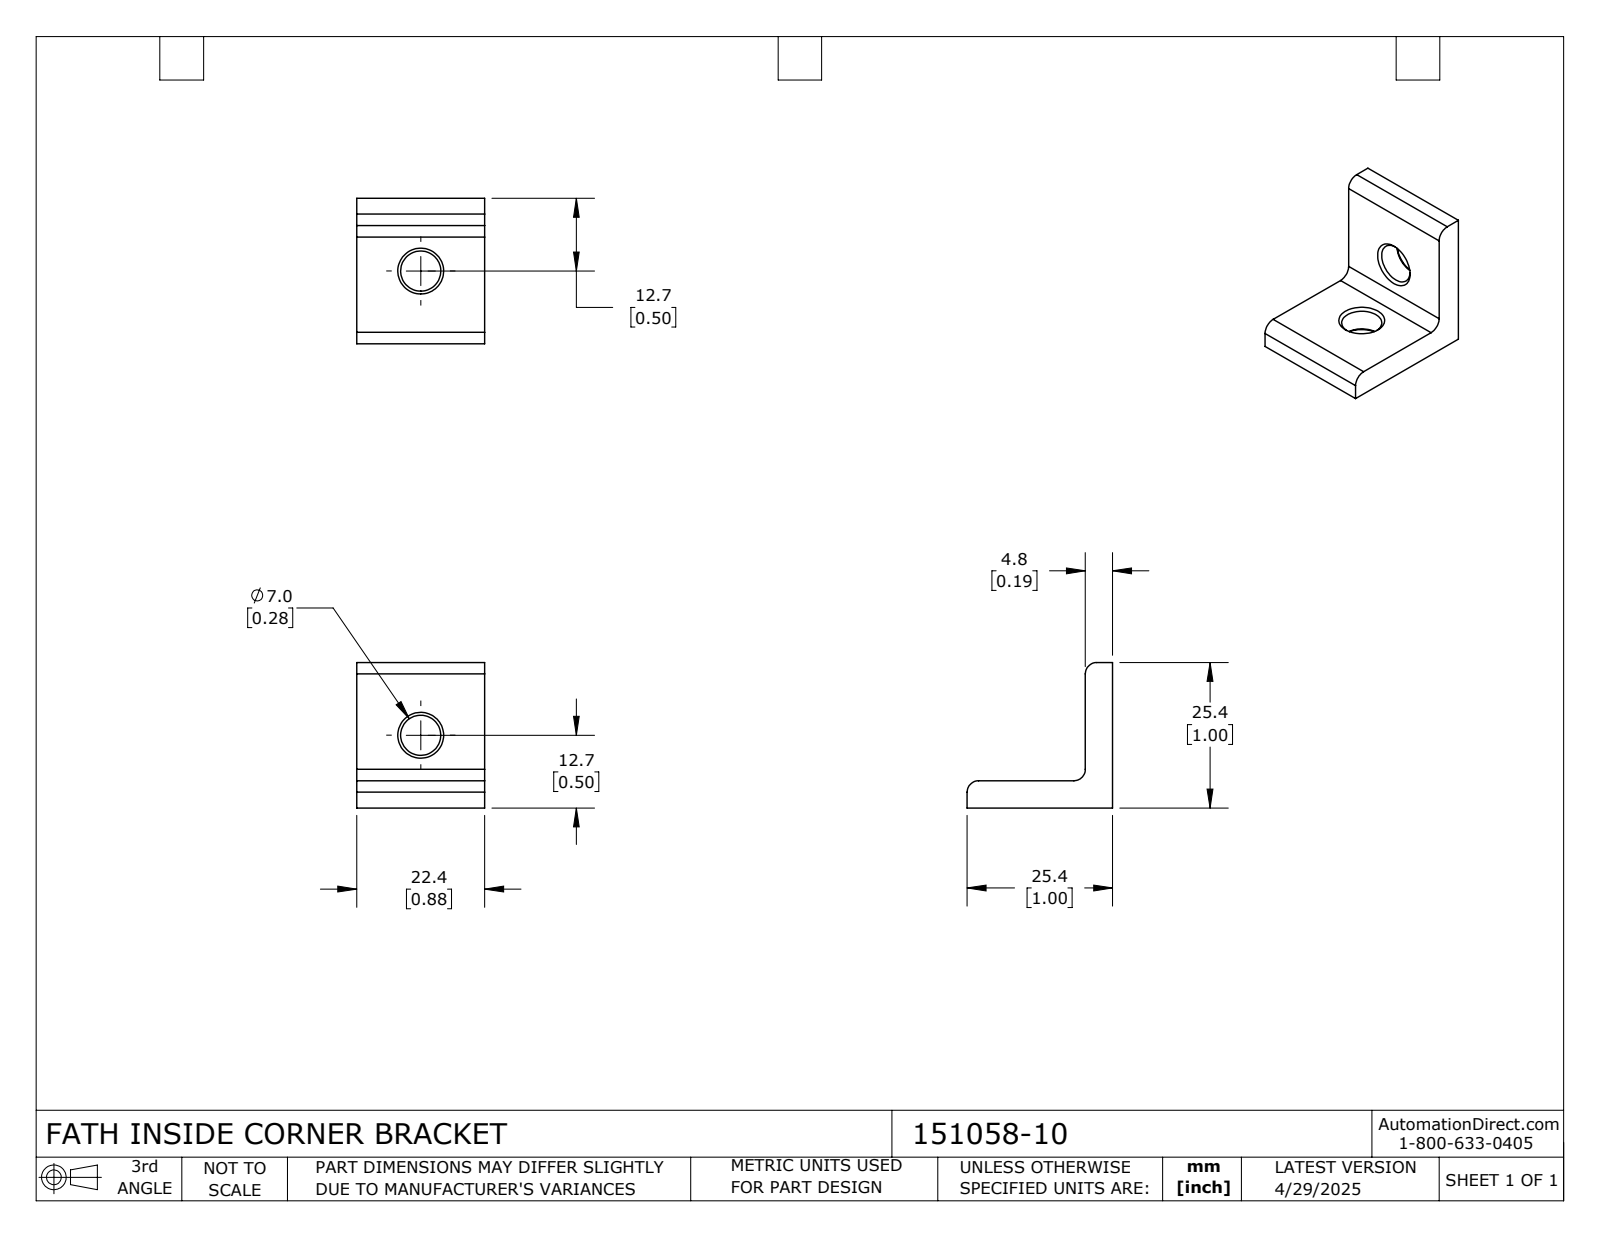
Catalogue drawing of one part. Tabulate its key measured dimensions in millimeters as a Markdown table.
| quantity | value |
| --- | --- |
| part name | 151058-10 |
| STEP written by | SolidWorks 2024 (CONFIG_CONTROL_DESIGN) |
| units | millimeters |
| bodies | 1 solid, 23 faces (8 planar, 7 cylindrical, 8 other) |
| overall size | 25.4 × 25.4 × 22.4 |
| volume | 4 510 mm³ |
| surface area | 2 681 mm² |
| round holes (diameter × count) | 7 × 2 |
| partial cylindrical surfaces (radius × count) | 2 × 3 |
| main face-to-face distances | 4.7, 22.4, 25.4, 20.7 |
